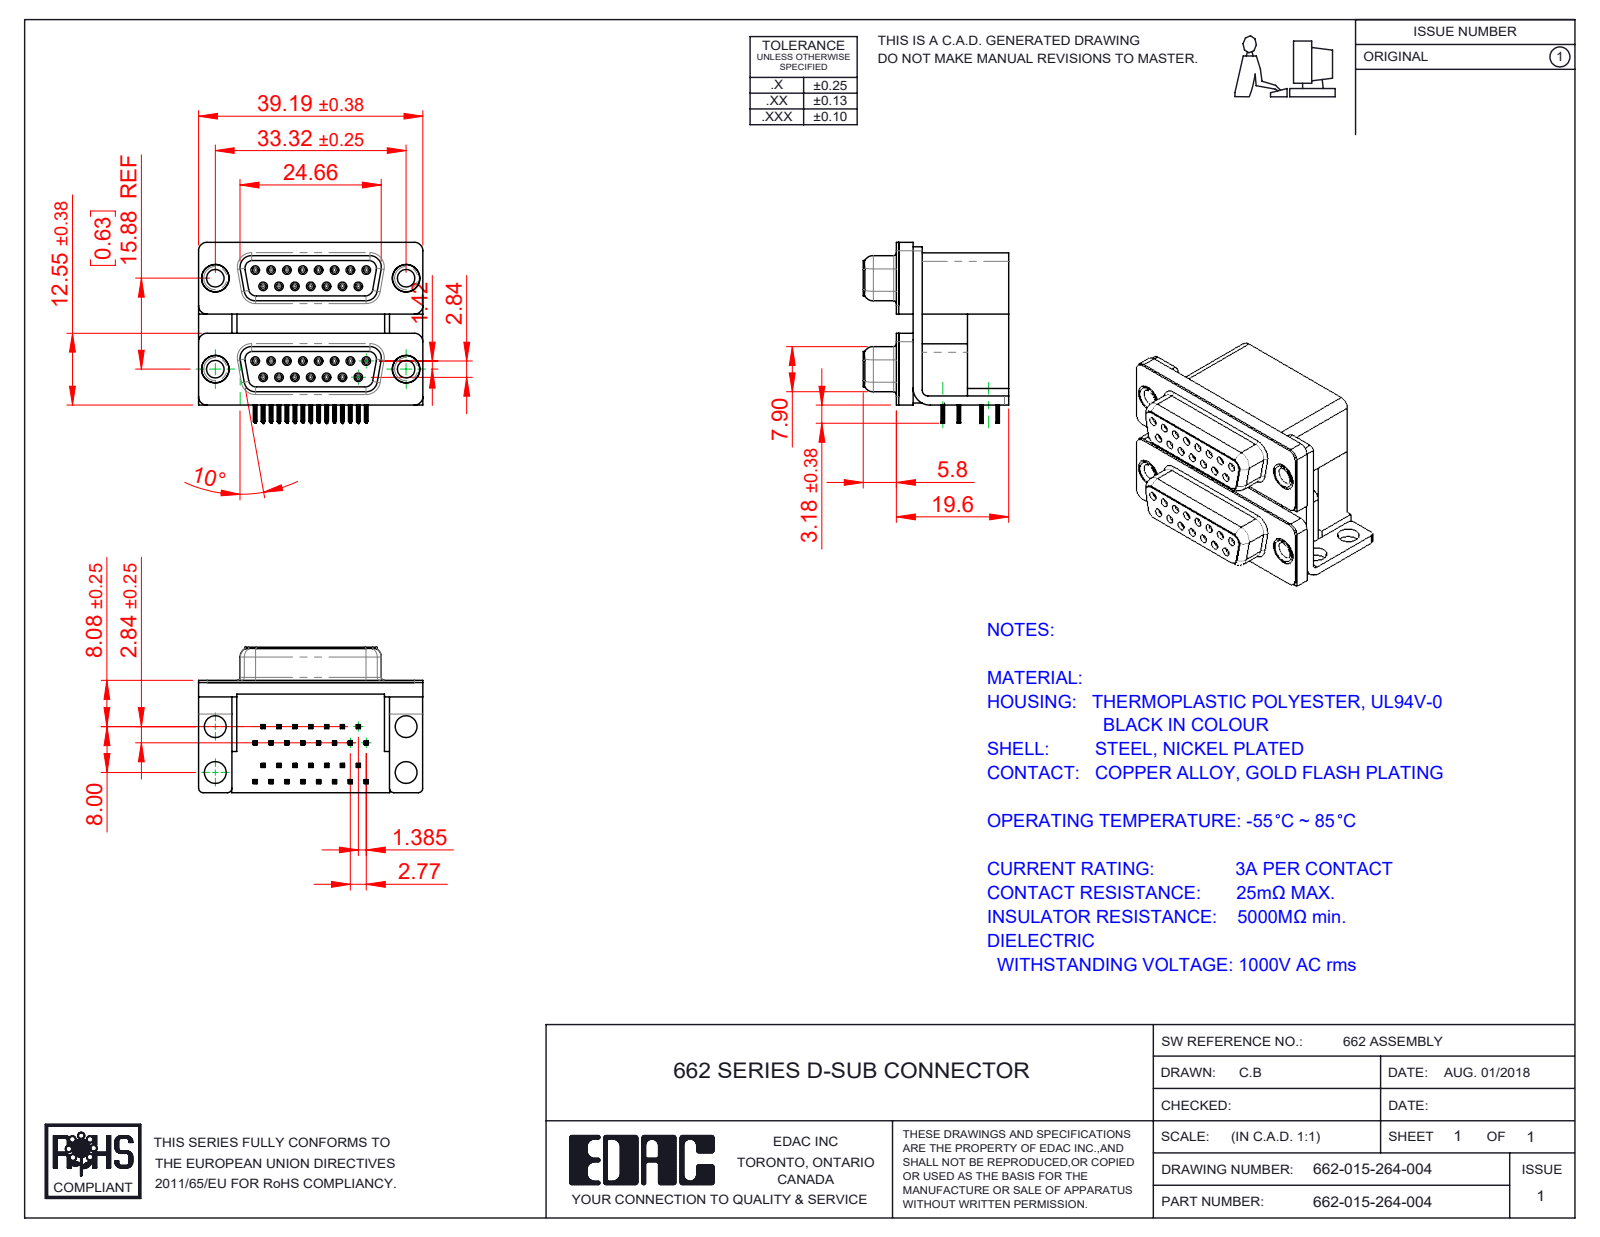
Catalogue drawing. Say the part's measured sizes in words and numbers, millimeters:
The part is named "662 Housing Spacer_15 Contacts L; 662 Contact Top Lower; 662-015-264-004; 662 Contact Bottom Upper_L (+7 more)". Its 3-D file was written by "SolidWorks 2020 (CONFIG_CONTROL_DESIGN)". It is 41 solids with 4778 faces: 2196 planar, 1138 cylindrical and 1444 other. Overall it measures 39.19 by 31.61 by 25.4 millimeters. Its volume is 15 328 cubic millimeters and its surface area 17 250 square millimeters. Round holes: 30 of diameter 0.8, 30 of diameter 0.9, 4 of diameter 3.05, 4 of diameter 3.5, 4 of diameter 3.8, 4 of diameter 4, 4 of diameter 4.8, 4 of diameter 5. Round bosses or shafts: 30 of diameter 1.2, 4 of diameter 4.9, 4 of diameter 4.75, 4 of diameter 3.85. Partial cylindrical surfaces (rounded edges, fillets, slot ends): 240 of radius 0.1, 120 of radius 0.15, 60 of radius 0.35, 30 of radius 0.34, 16 of radius 1.35, 15 of radius 1.5, 14 of radius 0.28, 8 of radius 0.5. The main face-to-face distances are 0.4, 19.2, 16.7, 2.5, 10.7, 2.9, 15.88, 7.2, 9.5, 12. The hole center spacings are 3.16, 16.12, 2.77, 16.82, 5.54, 8.31, 15.88, 17.92.
